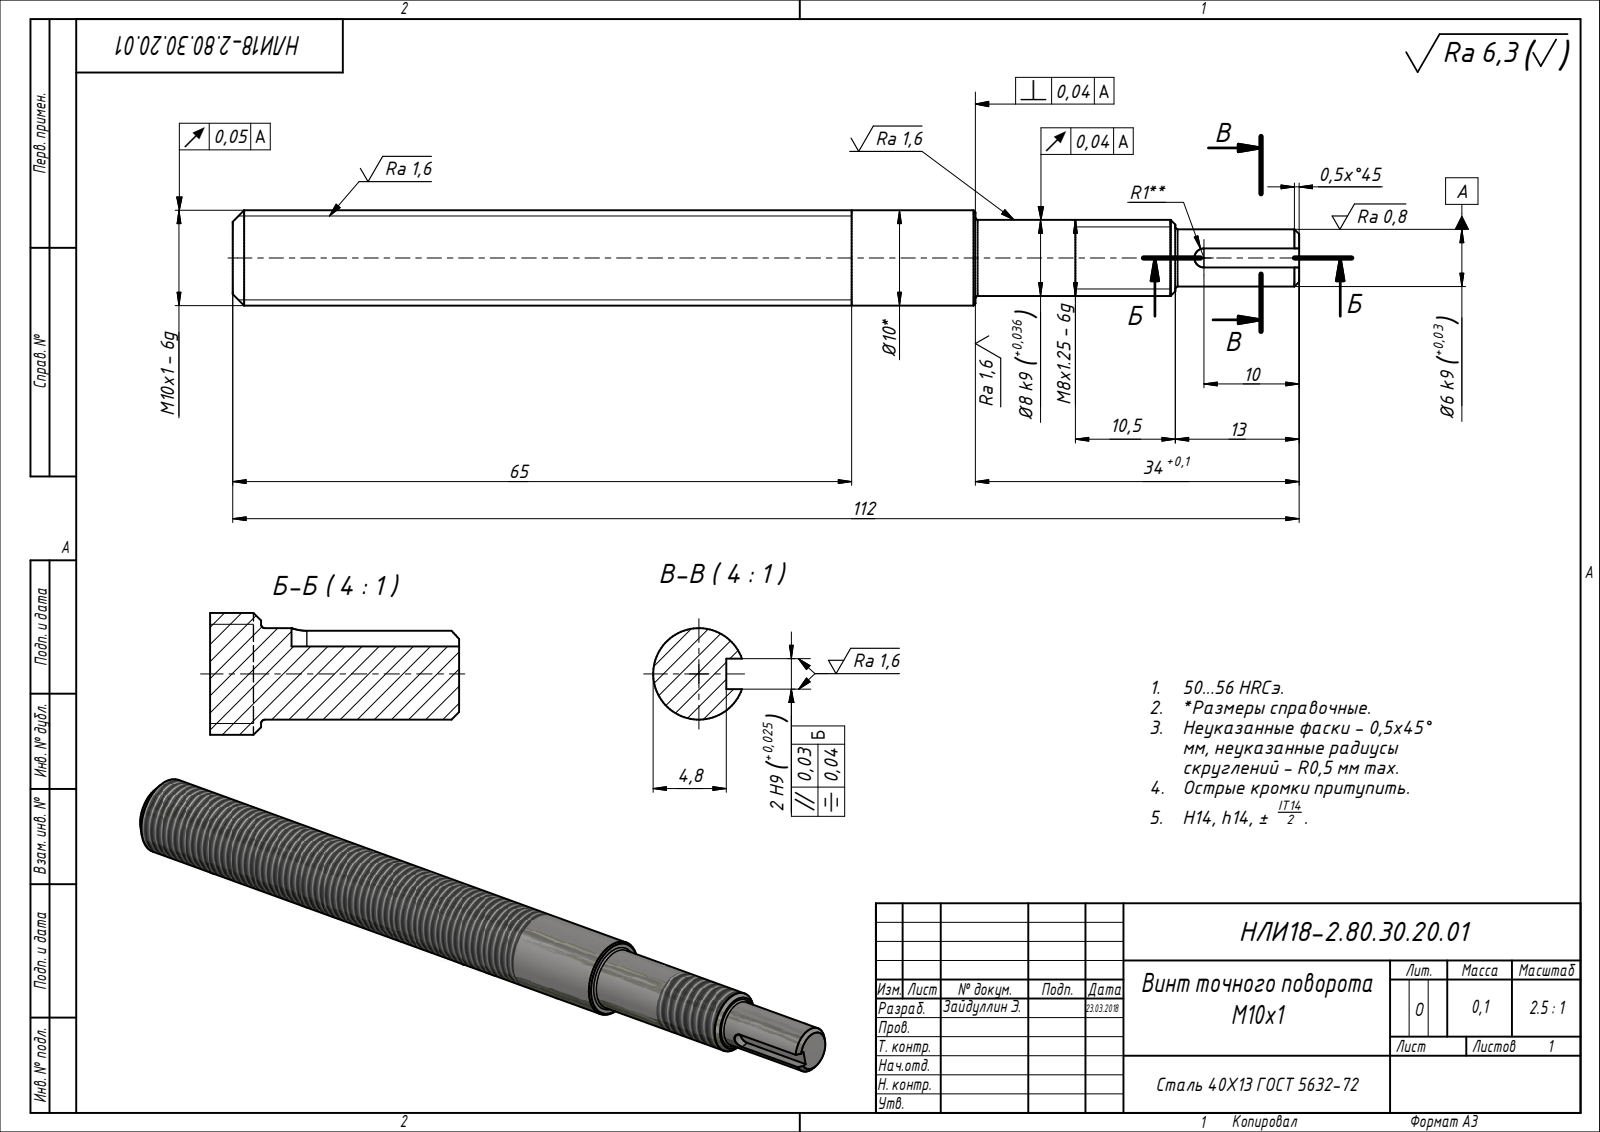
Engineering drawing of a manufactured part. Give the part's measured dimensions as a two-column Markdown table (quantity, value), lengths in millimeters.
| quantity | value |
| --- | --- |
| part name | НЛИ18-2.80.30.20.01. Винт \\X2\\0442043E0447043D043E0433043E\\X0\\ поворота М10х1 |
| STEP written by | Autodesk Inventor 2015 (AUTOMOTIVE_DESIGN) |
| units | millimeters |
| bodies | 1 solid, 17 faces (7 planar, 4 cylindrical, 6 other) |
| overall size | 112 × 10 × 10 |
| volume | 7 499 mm³ |
| surface area | 3 356 mm² |
| round bosses / shafts (diameter × count) | 10 × 1, 8 × 1, 6 × 1 |
| partial cylindrical surfaces (radius × count) | 1 × 1 |
| main face-to-face distances | 112, 78, 34, 2, 99, 21, 13 |
